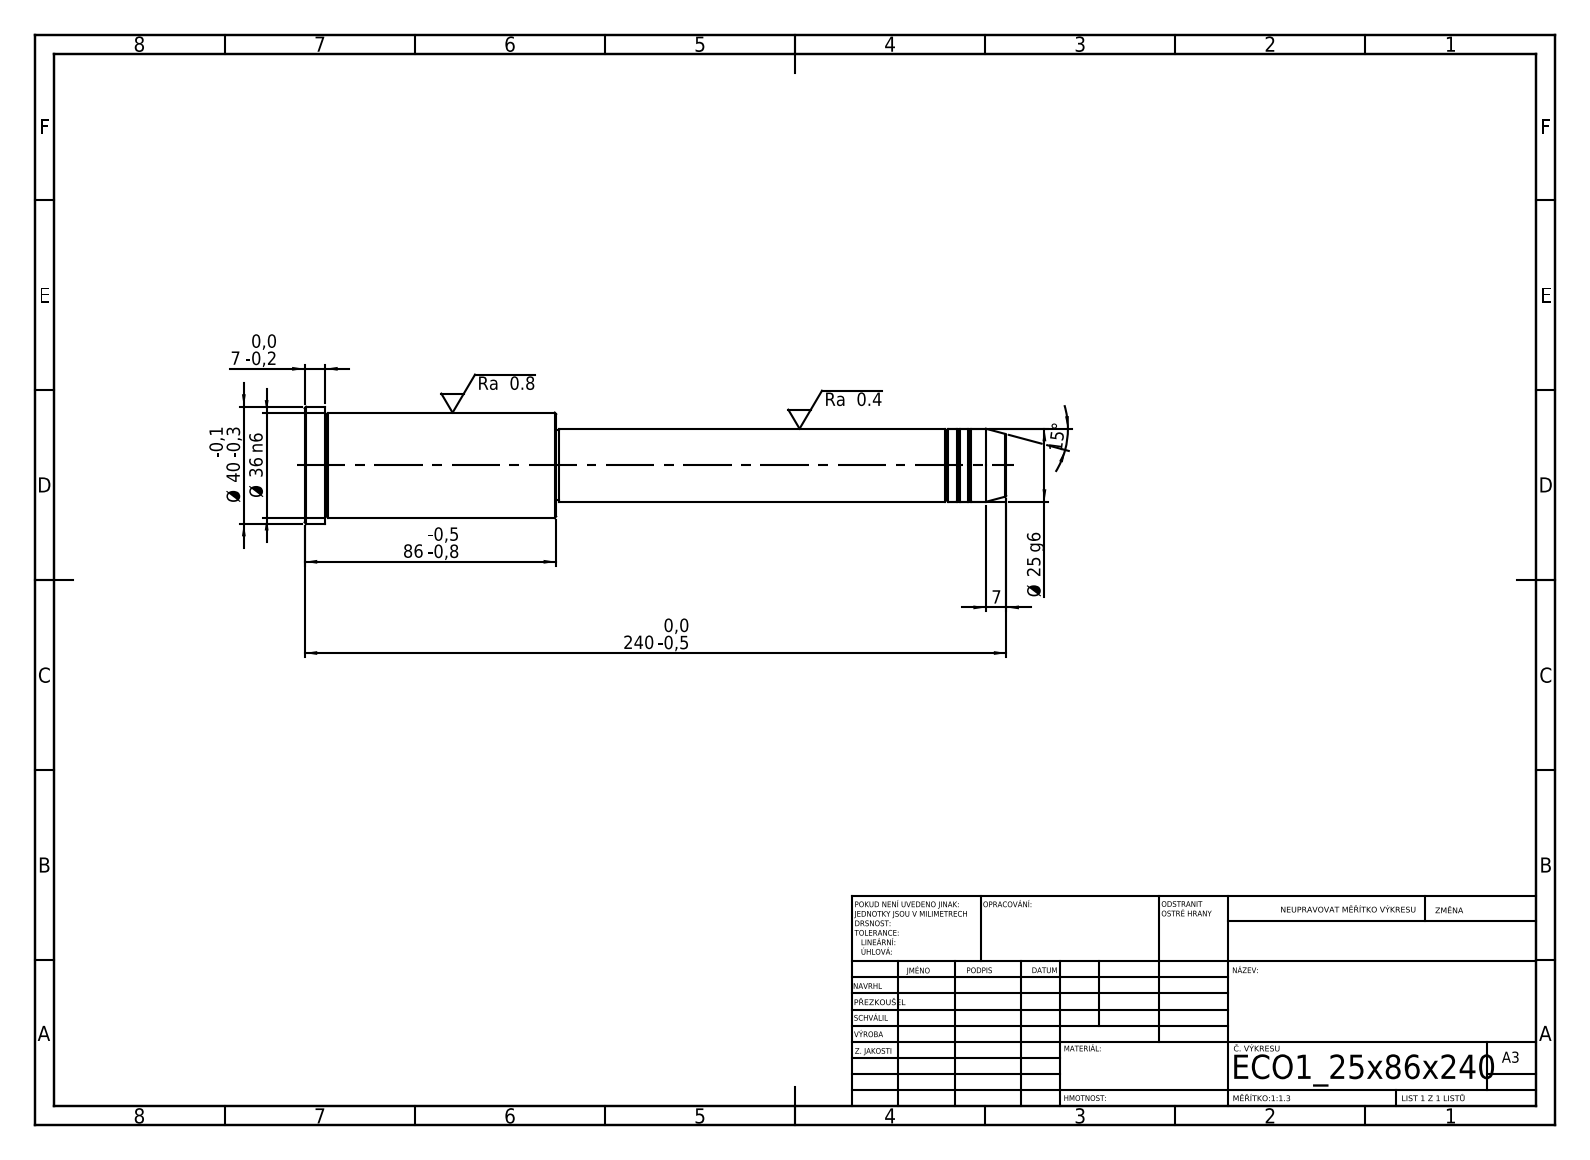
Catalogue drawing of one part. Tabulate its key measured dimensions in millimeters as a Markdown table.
| quantity | value |
| --- | --- |
| STEP written by | SolidWorks 2019 (CONFIG_CONTROL_DESIGN) |
| units | millimeters |
| bodies | 1 solid, 43 faces (5 planar, 14 cylindrical, 24 other) |
| overall size | 240 × 40 × 40 |
| volume | 164 109 mm³ |
| surface area | 24 445 mm² |
| round bosses / shafts (diameter × count) | 40 × 1, 36 × 1, 25 × 1, 24 × 1 |
| main face-to-face distances | 86, 154, 240, 233, 79, 7, 153, 1, 80, 87 |
